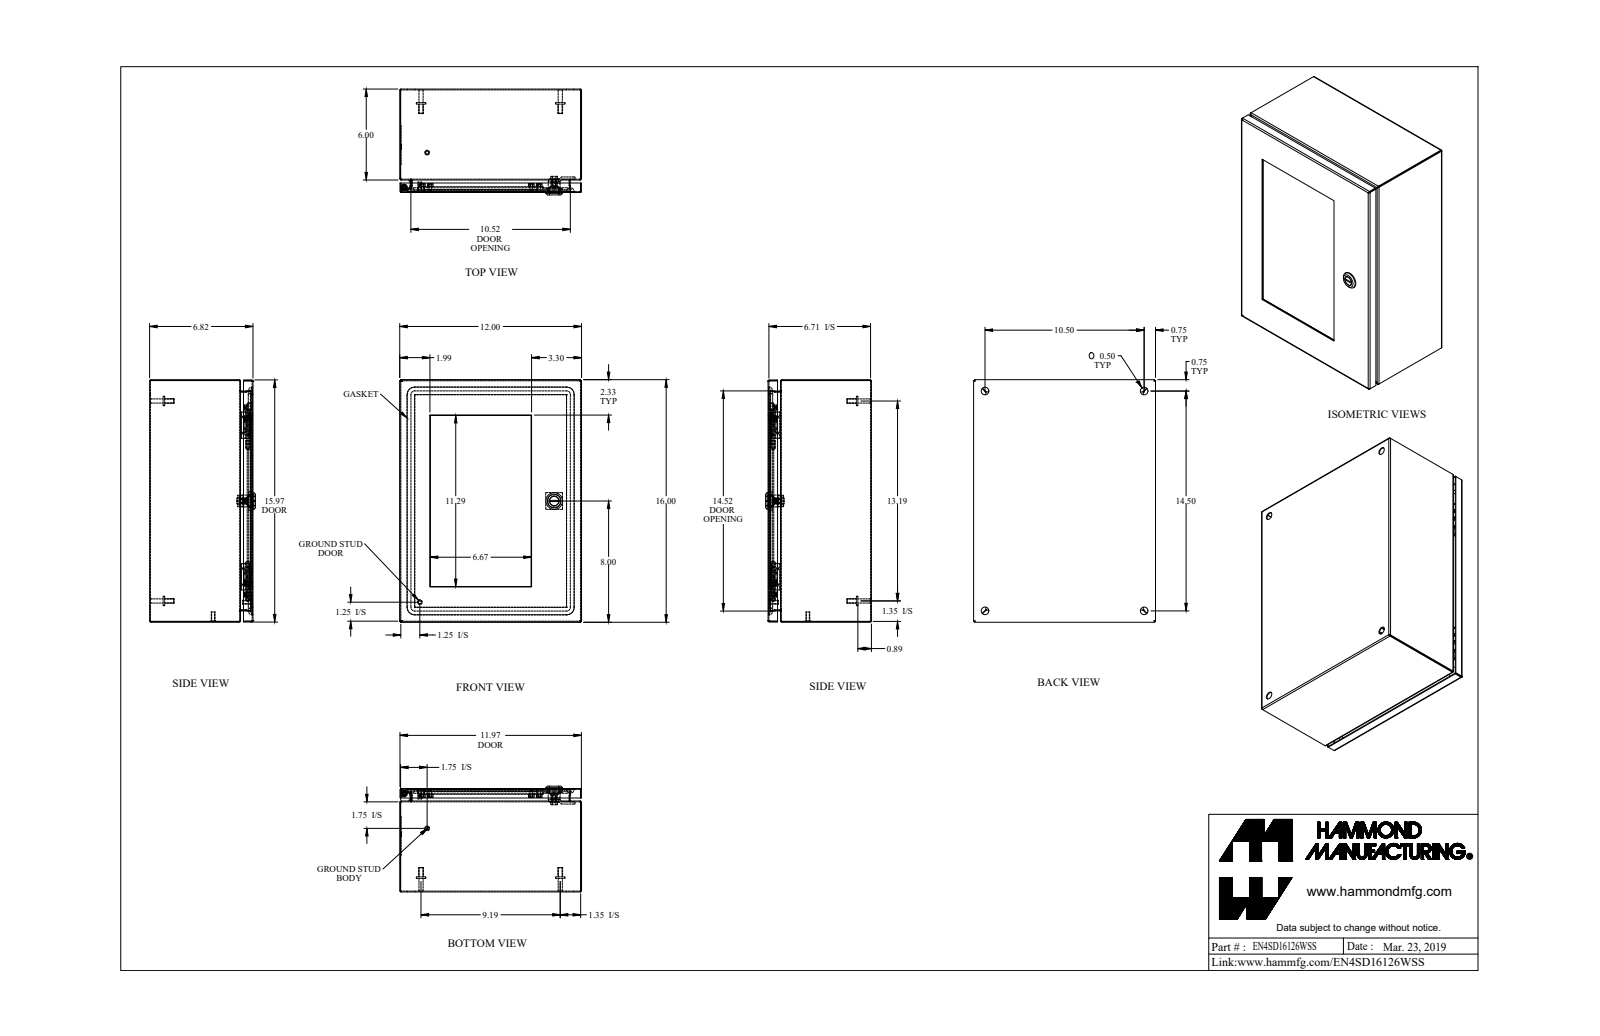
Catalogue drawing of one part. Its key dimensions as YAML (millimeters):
part_name: "EN4SD16126WSS_Default"
step_written_by: "SolidWorks 2019 (CONFIG_CONTROL_DESIGN)"
units: millimeters
bodies: {solids: 51, faces: 1083, planar: 544, cylindrical: 327, other: 212}
overall_size: [406.4, 304.8, 177.3]
volume: 1206000
surface_area: 1253000
round_holes:
  - {diameter: 3.3, count: 10}
  - {diameter: 6.4, count: 10}
  - {diameter: 12.7, count: 5}
  - {diameter: 4.4, count: 1}
  - {diameter: 5, count: 1}
  - {diameter: 6.1, count: 1}
  - {diameter: 6.1, count: 1}
  - {diameter: 9.8, count: 1}
  - {diameter: 16, count: 1}
  - {diameter: 19.5, count: 1}
round_bosses_or_shafts:
  - {diameter: 5.7, count: 11}
  - {diameter: 9.3, count: 10}
  - {diameter: 4.2, count: 10}
  - {diameter: 8, count: 6}
  - {diameter: 15.9, count: 5}
  - {diameter: 7, count: 4}
  - {diameter: 6.4, count: 2}
  - {diameter: 27.9, count: 1}
partial_cylinders:
  - {radius: 0.7, count: 21}
  - {radius: 2.2, count: 21}
  - {radius: 4.8, count: 12}
  - {radius: 3.2, count: 10}
  - {radius: 0.2, count: 4}
  - {radius: 0.4, count: 4}
  - {radius: 1.6, count: 4}
  - {radius: 2.2, count: 4}
face_to_face_distances: [1.4, 171.8, 170.4, 303.4, 405, 6.4, 173.3, 7.8, 164, 165.5]
hole_center_spacings: [138.1, 138.1, 276.2, 22.7, 22.7, 157.2, 157.2, 183.5]
